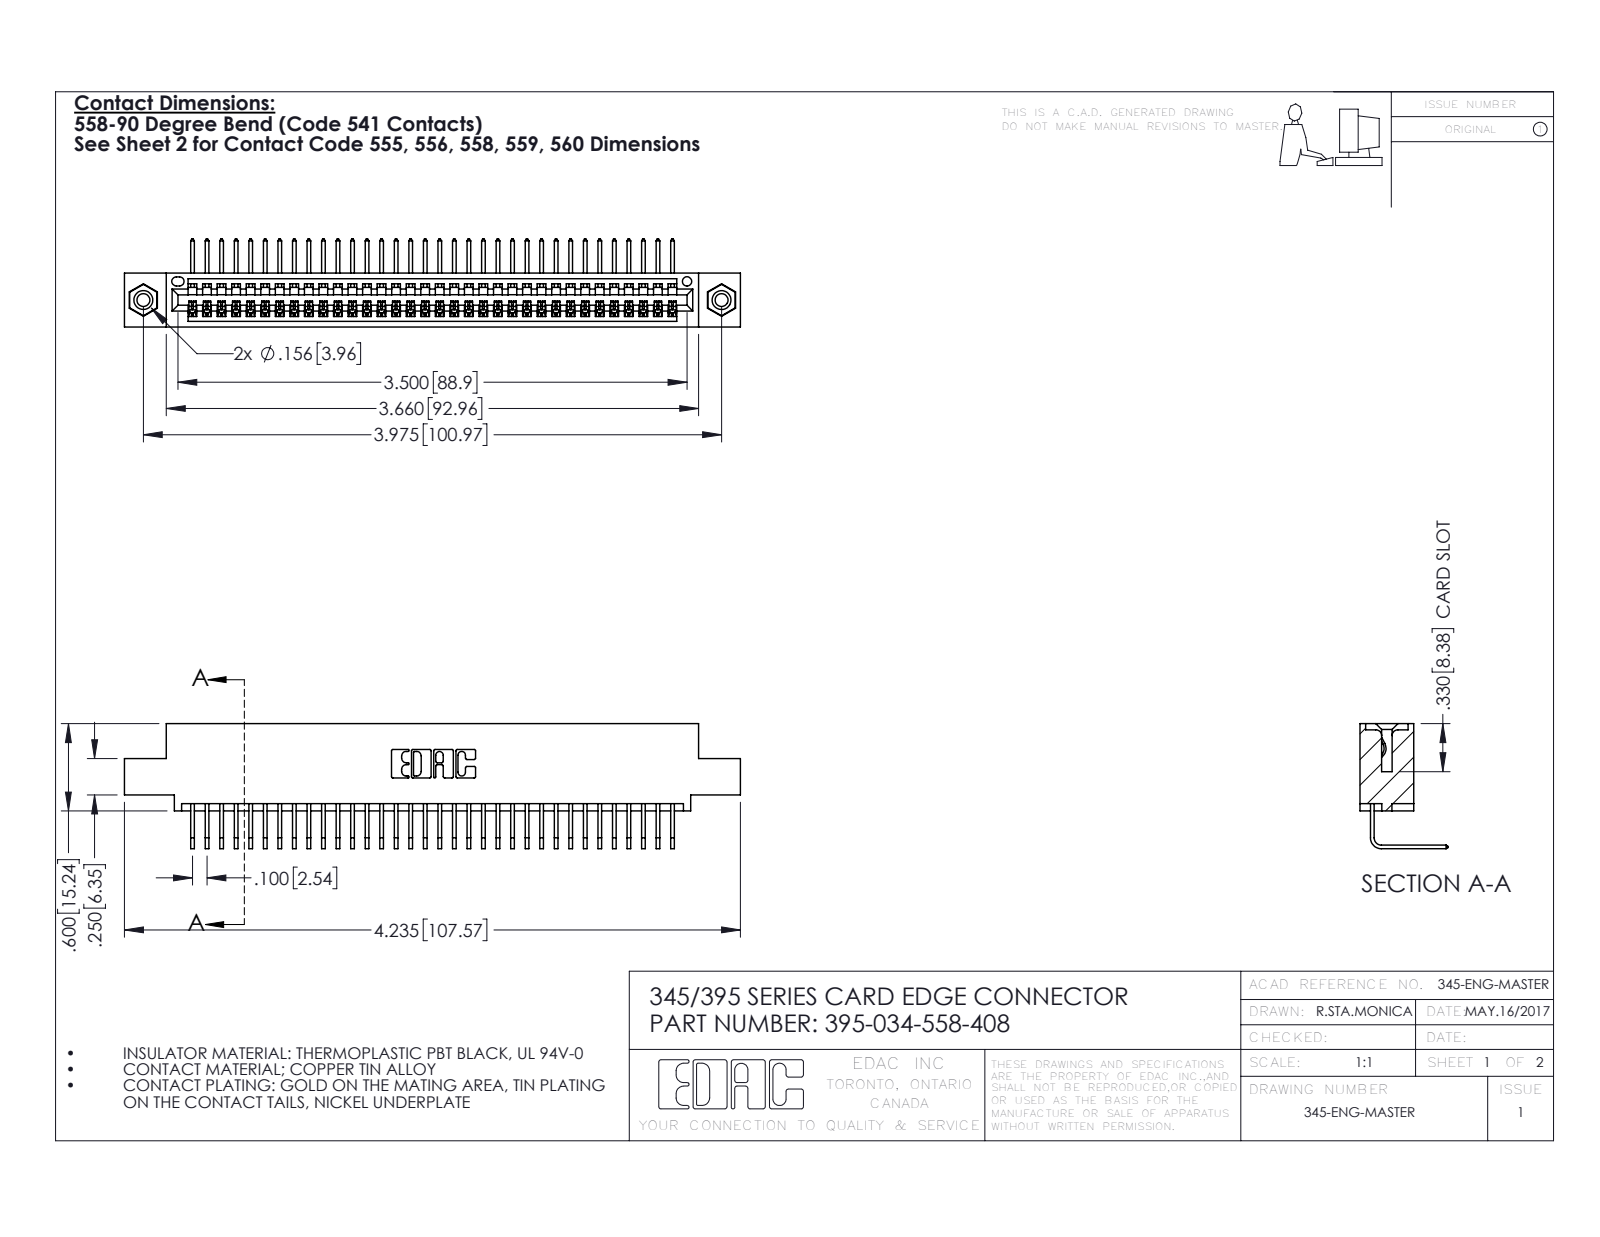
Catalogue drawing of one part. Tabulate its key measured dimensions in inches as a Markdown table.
| quantity | value |
| --- | --- |
| part name | 345-292-001_558 Tail - 2; 395-034-558-408; 345-250-001_345-250-003-102; 345 Part_0.110 Offset - 0.156 Dia-TI |
| STEP written by | SolidWorks 2016 (CONFIG_CONTROL_DESIGN) |
| units | inches |
| bodies | 37 solids, 2230 faces (1544 planar, 670 cylindrical, 16 other) |
| overall size | 4.235 × 0.859 × 0.605 |
| volume | 0.622 in³ |
| surface area | 22 in² |
| round holes (diameter × count) | 0.089 × 2, 0.125 × 2, 0.156 × 2, 0.064 × 1 |
| round bosses / shafts (diameter × count) | 0.155 × 2 |
| partial cylindrical surfaces (radius × count) | 0.006 × 68, 0.01 × 22, 0.007 × 6, 0.031 × 6, 0.026 × 3, 0.031 × 2, 0.04 × 2, 0.014 × 1 |
| main face-to-face distances | 0.072, 0.298, 0.37, 0.2, 0.098, 0.272, 0.025, 0.225, 0.149, 0.072 |
| hole center spacings | 0.27, 3.74, 3.975 |
